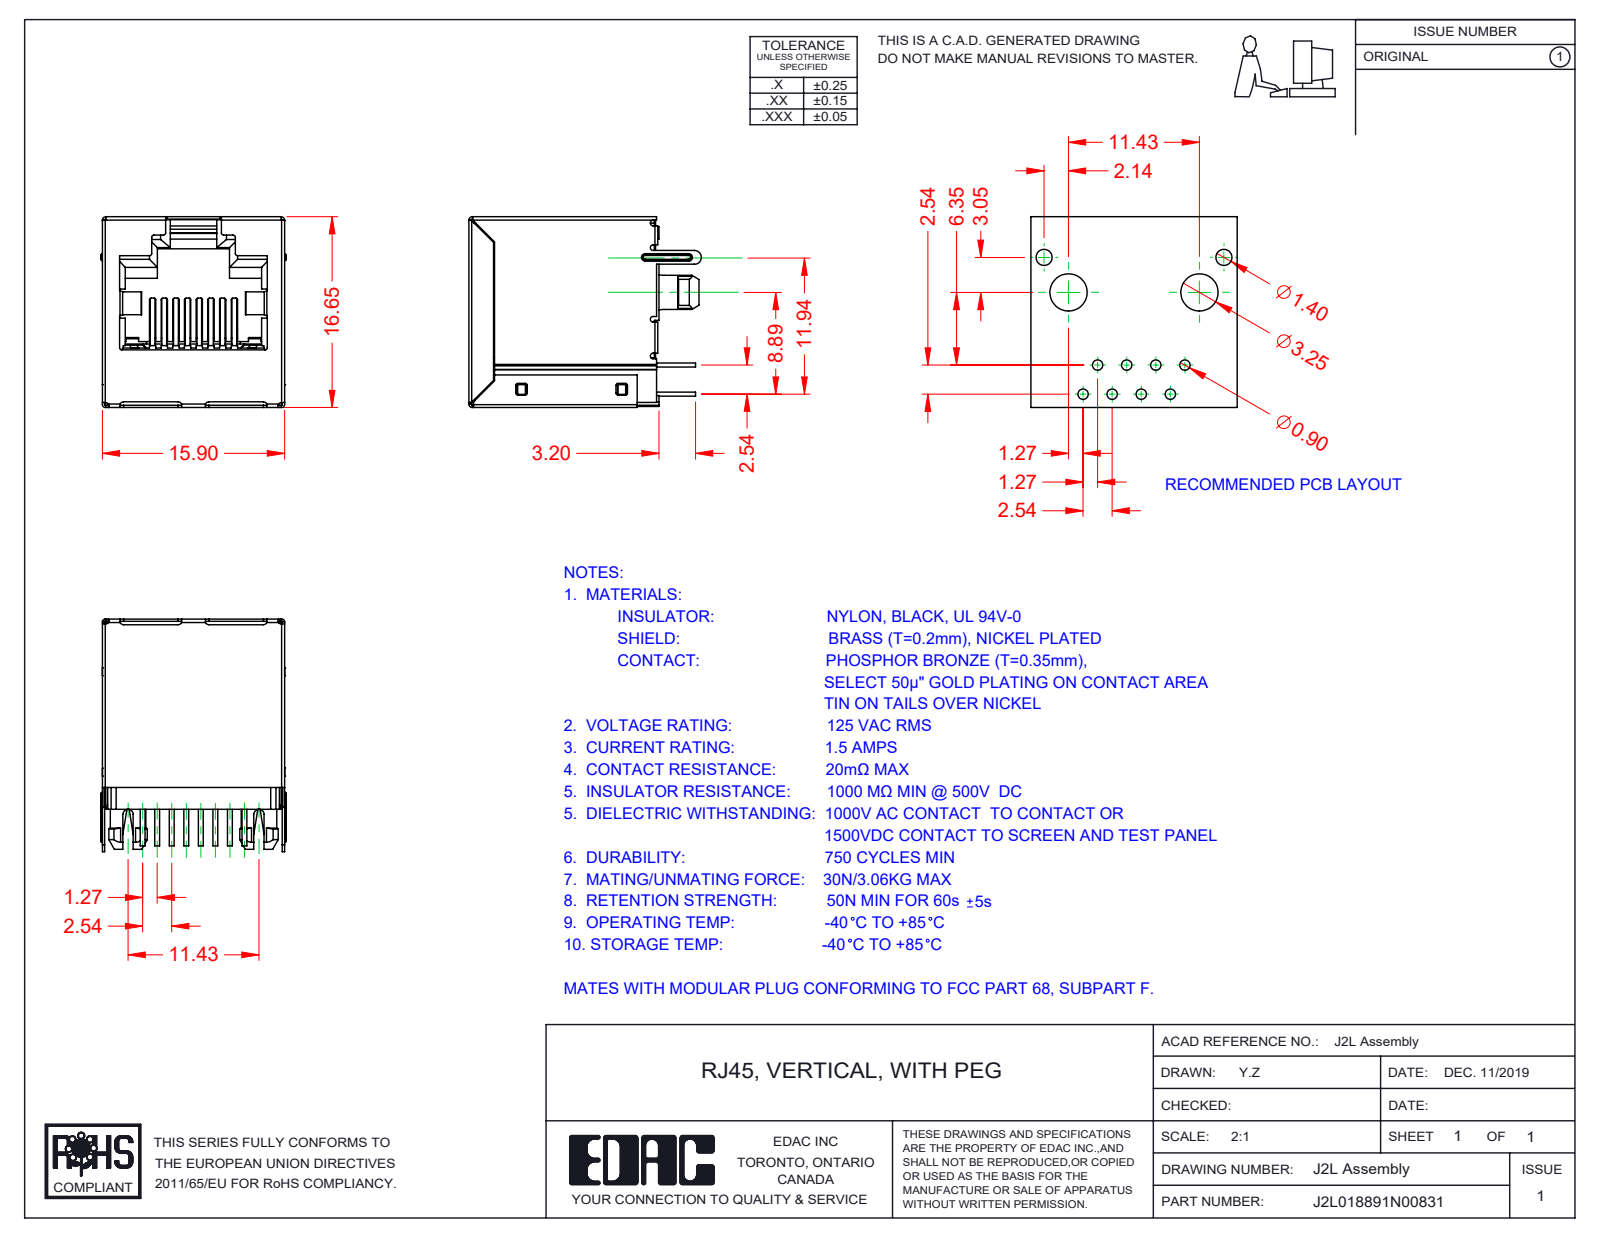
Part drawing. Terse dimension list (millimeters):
name: 2L Mylar Tape; 2L Contacts; 2L Shield; 2L Contact Lock (+2 more)
written by: SolidWorks 2016 (CONFIG_CONTROL_DESIGN)
unit: mm
bodies: 12 solids, 1131 faces (784 planar, 284 cylindrical, 63 other)
size: 20.3 × 16.65 × 16.2
volume: 2 735 mm³; area: 6 843 mm²
bosses: 2× ⌀3.1, 2× ⌀1.1
rounds: 64× R0.15, 20× R0.25, 16× R0.2, 14× R0.3, 9× R0.35, 8× R0.1, 4× R0.28, 3× R0.5
face distances: 15.45, 15.7, 16.45, 16.2, 16.4, 15.65, 16.3, 16.25, 15.9, 15.5
